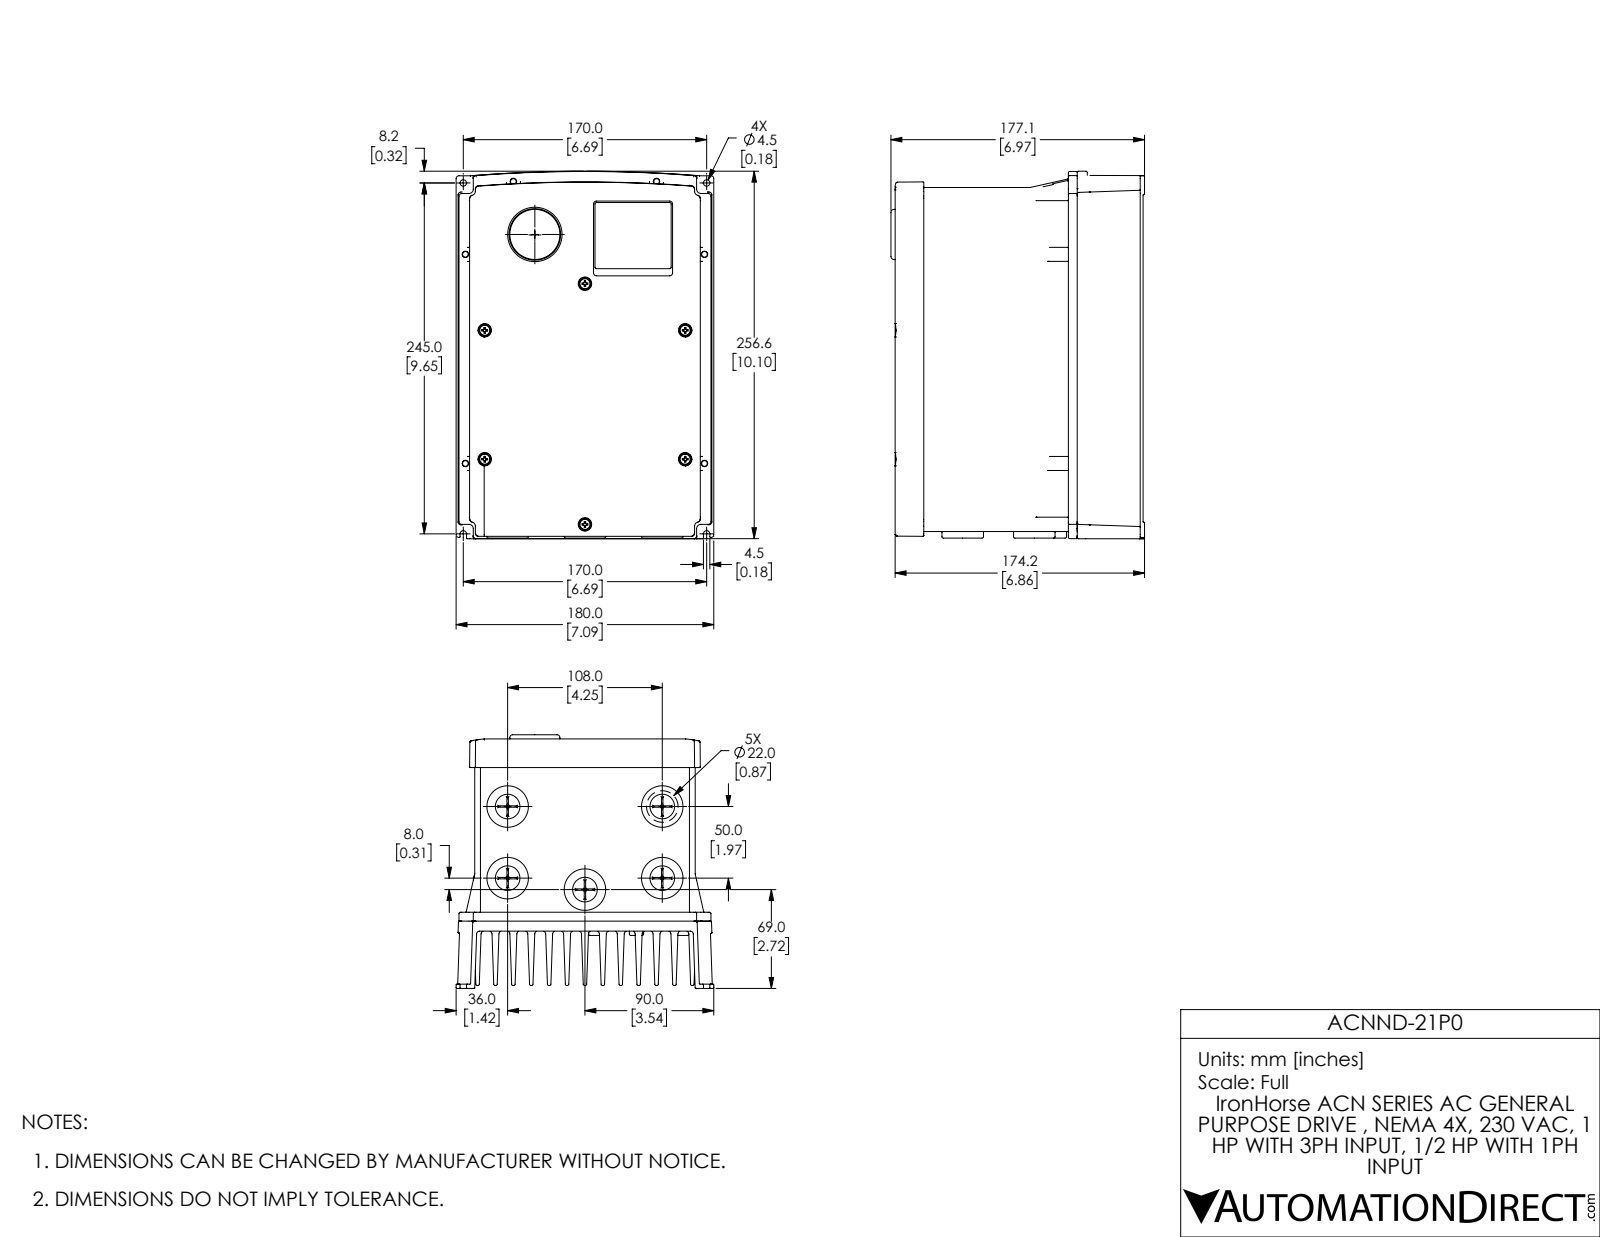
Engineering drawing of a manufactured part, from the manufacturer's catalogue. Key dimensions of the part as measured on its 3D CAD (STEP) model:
Part name (STEP PRODUCT): total_assy_ip66_008__asm 0210 B fXTb ext1C No Knob 1 COMPLETE SMaller 1
STEP written by: SolidWorks 2017 (AUTOMOTIVE_DESIGN)
Units: inches
Bodies: 2 solids, 2831 faces (876 planar, 918 cylindrical, 1037 other)
Overall size (bounding box): 10.103 × 7.087 × 6.972
Volume: 329 in³ · Surface area: 962.1 in²
Round holes (diameter × count): ⌀0.157 ×17, ⌀0.177 ×10, ⌀0.079 ×6, ⌀0.331 ×6, ⌀0.677 ×5, ⌀1.024 ×5, ⌀0.118 ×2, ⌀0.138 ×1, ⌀0.335 ×1, ⌀0.669 ×1, ⌀1.417 ×1
Round bosses / shafts (diameter × count): ⌀0.315 ×6, ⌀1.142 ×5, ⌀0.85 ×5, ⌀1.102 ×1, ⌀0.551 ×1, ⌀0.472 ×1, ⌀0.118 ×1
Partial cylindrical surfaces — rounded edges, fillets, slot ends (radius × count): R0.039 ×160, R0.02 ×122, R0.008 ×73, R0.079 ×70, R0.118 ×42, R0.197 ×6, R0.167 ×4, R0.236 ×3
Main face-to-face distances: 0.492, 1.967, 1.475, 2.458, 0.983, 0.983, 2.95, 3.441, 3.933, 4.425
Hole centre spacings: 2.362, 1.194, 2.363, 3.937, 5.315, 9.635, 10.106, 1.969
